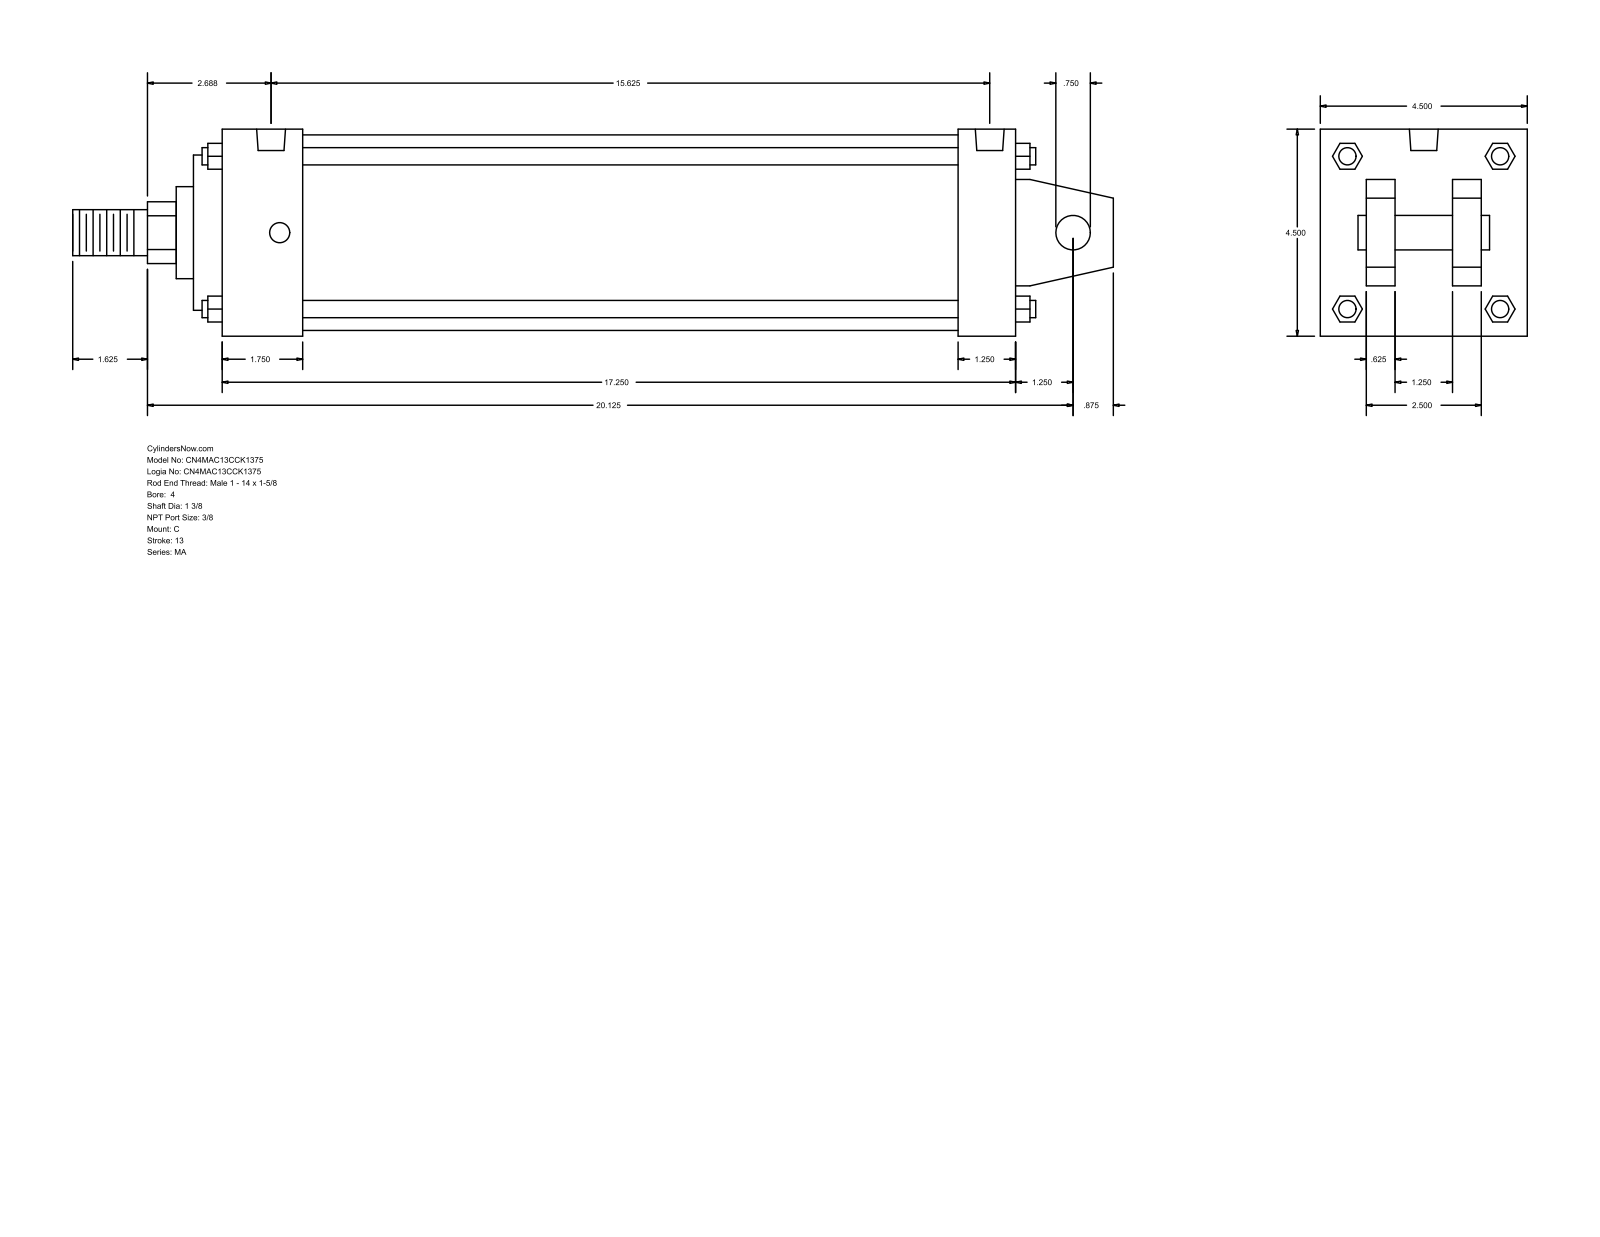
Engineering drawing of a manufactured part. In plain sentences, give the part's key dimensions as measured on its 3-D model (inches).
The part is named "MA_C__0400_1.375". Its 3-D file was written by "GSSL Pune (CONFIG_CONTROL_DESIGN)". It is 0 solids with 141 faces: 109 planar, 32 cylindrical and 0 other. Overall it measures 22.625 by 4.5 by 4.5 inches. Round holes: 4 of diameter 0.437, 2 of diameter 0.627. Round bosses or shafts: 4 of diameter 0.375, 1 of diameter 4.25, 1 of diameter 3.375, 1 of diameter 2, 1 of diameter 1.375, 1 of diameter 1, 1 of diameter 0.75. Partial cylindrical surfaces (rounded edges, fillets, slot ends): 1 of radius 0.672. The main face-to-face distances are 4.5, 0.625, 17.25, 2.875, 1.625, 1, 3.5, 1.875, 17.875, 16.625. The hole center spacings are 15.25, 0.187, 0.188, 15.437, 15.438, 15.625.
